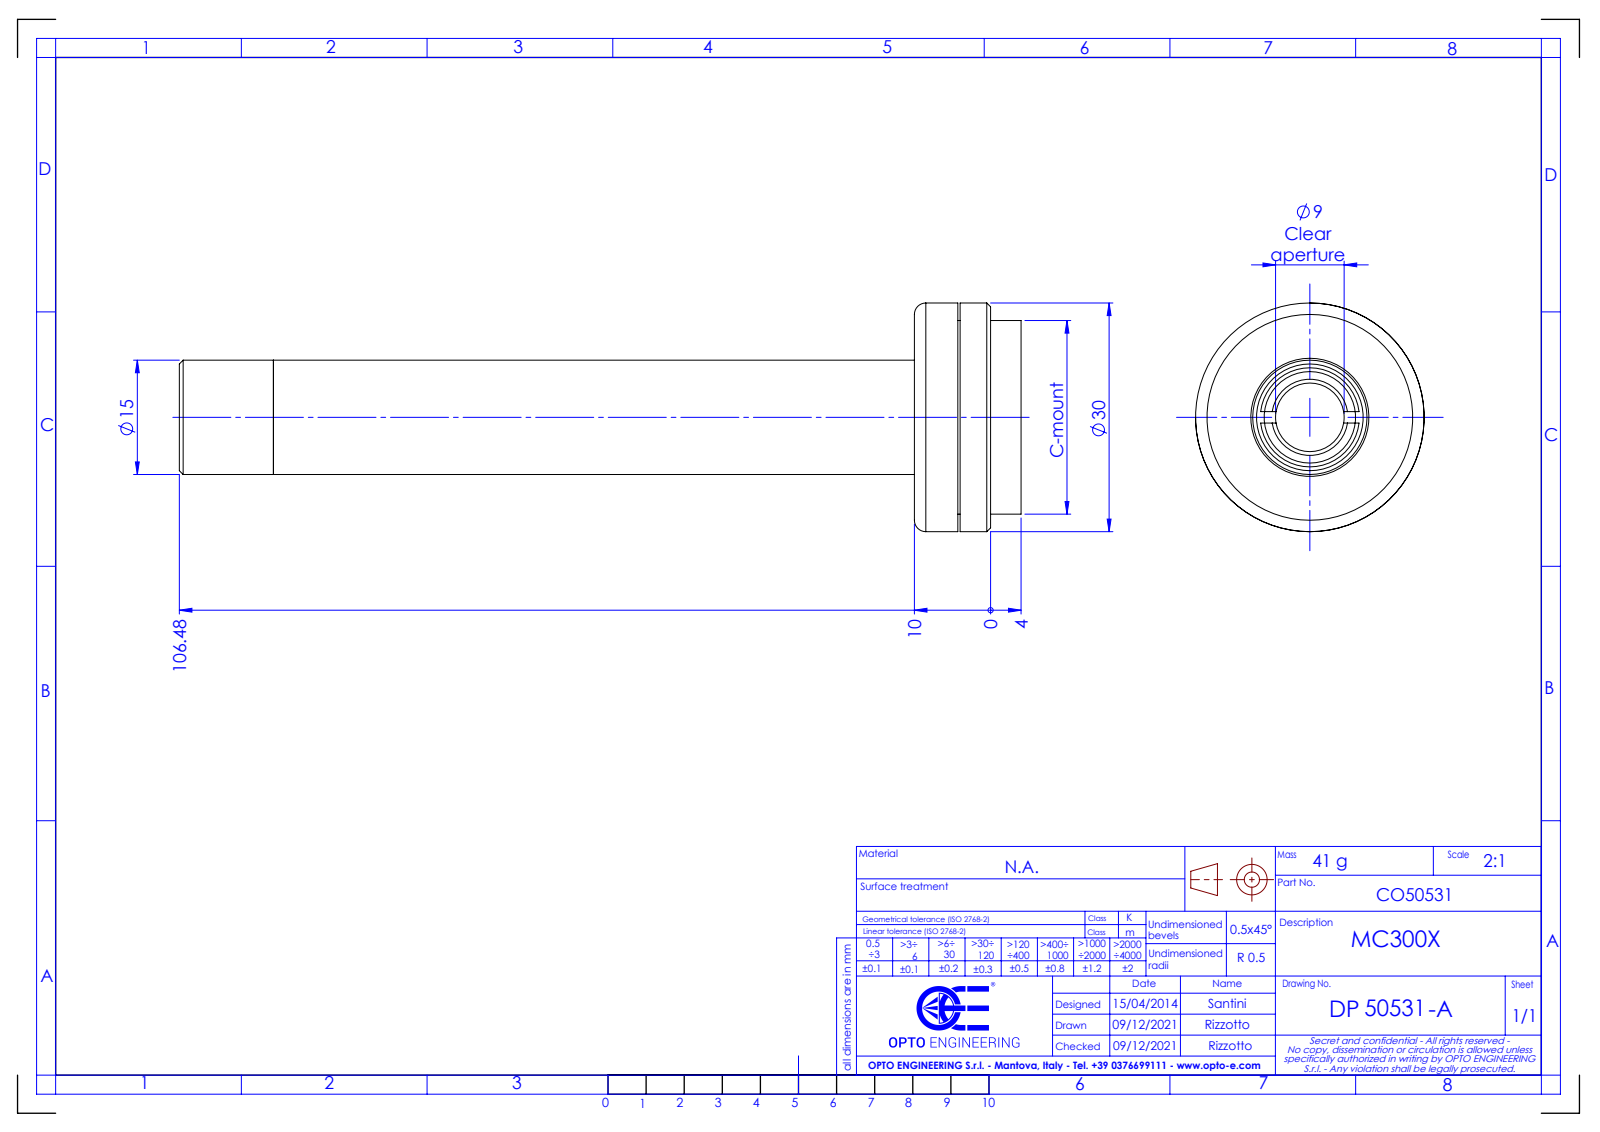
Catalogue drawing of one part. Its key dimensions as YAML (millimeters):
part_name: "DP50531-A_MC300X"
step_written_by: "SolidWorks 2021 (CONFIG_CONTROL_DESIGN)"
units: millimeters
bodies: {solids: 0, faces: 49, planar: 16, cylindrical: 18, other: 15}
overall_size: [110.48, 30, 30]
round_holes:
  - {diameter: 9, count: 1}
  - {diameter: 12, count: 1}
round_bosses_or_shafts:
  - {diameter: 30, count: 1}
  - {diameter: 25.4, count: 1}
  - {diameter: 15, count: 1}
  - {diameter: 14.5, count: 1}
face_to_face_distances: [4, 6, 5.7, 10, 4.3, 14, 8.3, 8, 96.48, 102.18]
